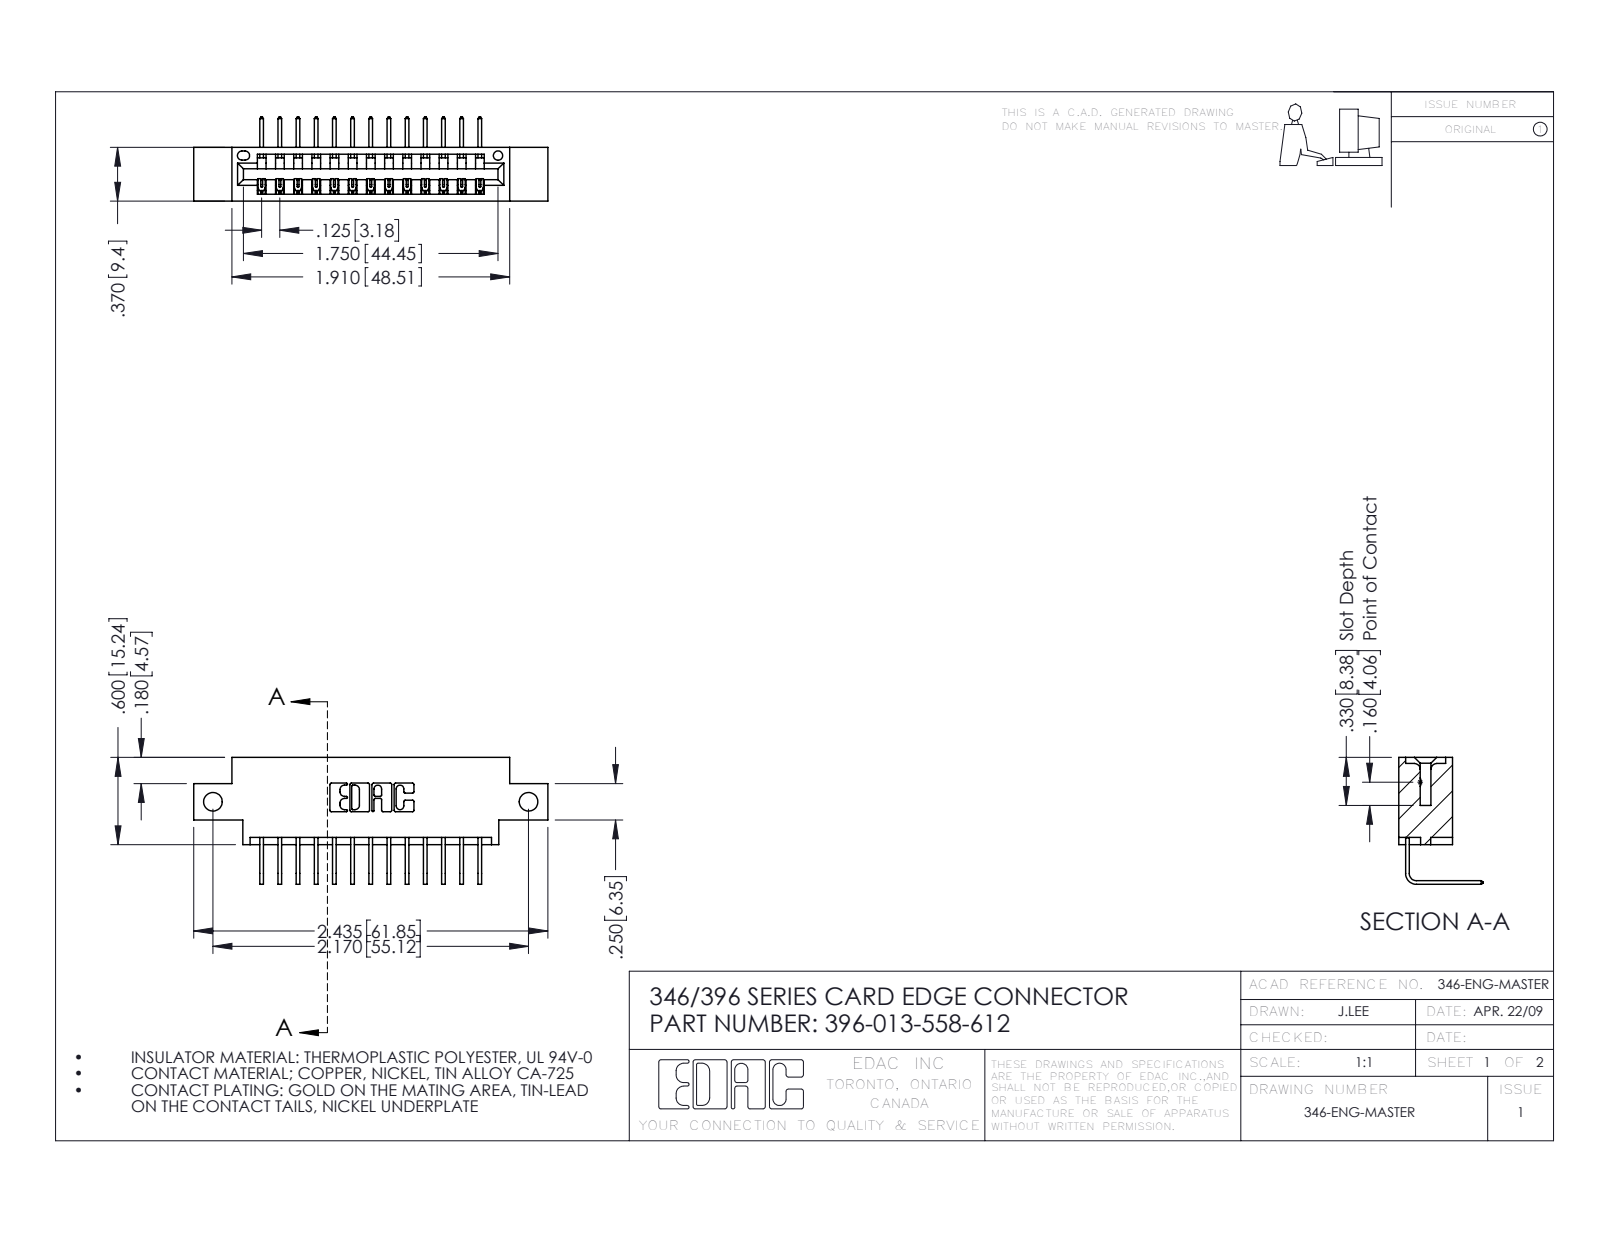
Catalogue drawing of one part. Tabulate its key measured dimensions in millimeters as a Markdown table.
| quantity | value |
| --- | --- |
| part name | 396-013-558-612; 345-292-001_558 Tail - 2; 346 Part_0.170 Offset - Side Mount |
| STEP written by | SolidWorks 2016 (CONFIG_CONTROL_DESIGN) |
| units | millimeters |
| bodies | 14 solids, 906 faces (626 planar, 280 cylindrical, 0 other) |
| overall size | 61.8 × 22.2 × 14.7 |
| volume | 5 520 mm³ |
| surface area | 6 865 mm² |
| round holes (diameter × count) | 3.3 × 2, 1.6 × 1 |
| partial cylindrical surfaces (radius × count) | 0.2 × 26, 0.3 × 22, 0.2 × 6, 0.8 × 6, 0.7 × 3, 0.8 × 2, 1 × 2, 0.4 × 1 |
| main face-to-face distances | 8.2, 6.4, 9.4, 1.2, 7.6, 0.6, 1.8, 3.8, 5.6, 2.5 |
| hole center spacings | 55.1 |
